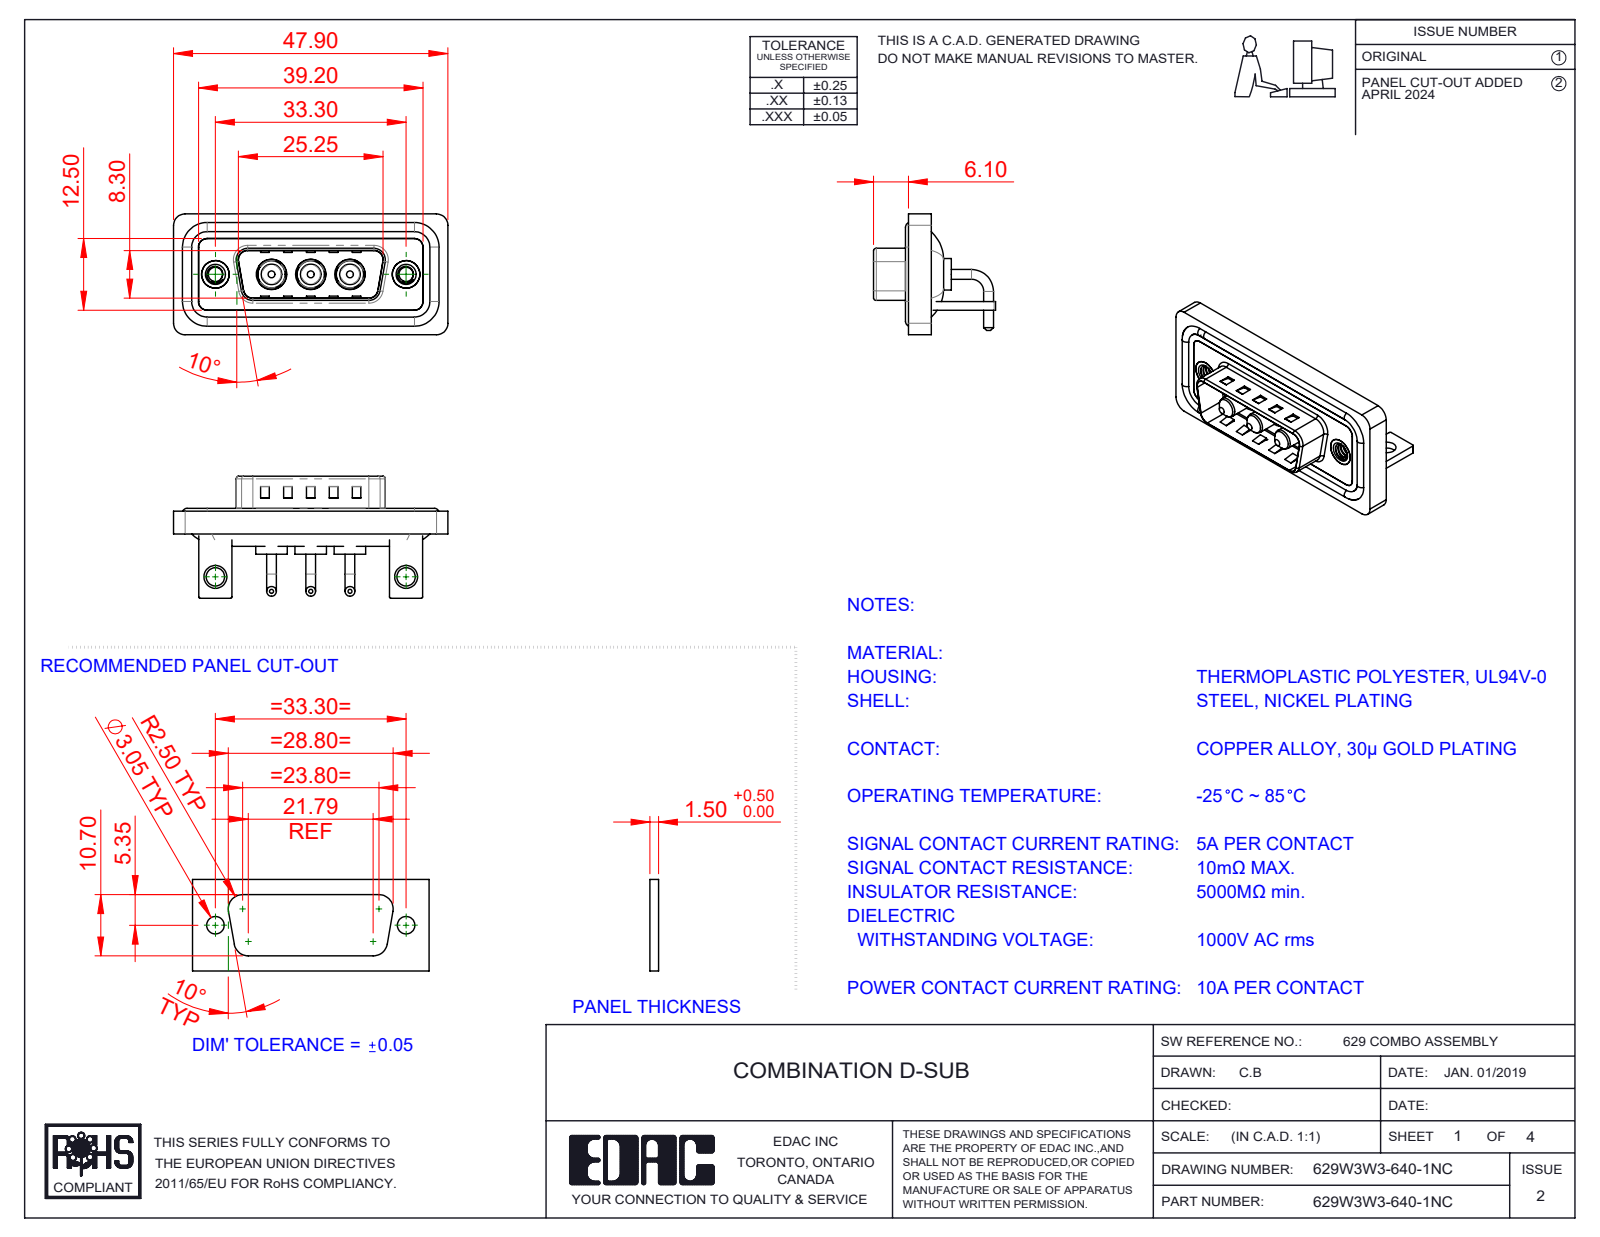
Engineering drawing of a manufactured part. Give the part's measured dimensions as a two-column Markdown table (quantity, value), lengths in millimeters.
| quantity | value |
| --- | --- |
| part name | 629Combo Stabilizer Bracket; 629Combo Housing_3W3; 629Combo Shell Rear_15 Contacts; Power Pin_10A RA (+4 more) |
| STEP written by | SolidWorks 2023 (CONFIG_CONTROL_DESIGN) |
| units | millimeters |
| bodies | 15 solids, 614 faces (227 planar, 265 cylindrical, 122 other) |
| overall size | 47.9 × 21.3 × 21.1 |
| volume | 5 876 mm³ |
| surface area | 9 471 mm² |
| round holes (diameter × count) | 4.85 × 3, 5.3 × 3, 2.5 × 2, 3.2 × 2, 4 × 2, 4.8 × 2, 5 × 2 |
| round bosses / shafts (diameter × count) | 1.7 × 6, 1.6 × 4, 5.5 × 3, 5.2 × 3, 4.75 × 3, 3.75 × 3, 3.6 × 3, 4.9 × 2 |
| partial cylindrical surfaces (radius × count) | 2 × 21, 1.5 × 18, 0.25 × 16, 0.5 × 9, 1.6 × 8, 0.6 × 4, 0.65 × 4, 0.9 × 4 |
| main face-to-face distances | 0.4, 1.5, 0.8, 2.9, 1.1, 2.1, 3.7, 1.6, 1.2, 4.5 |
| hole center spacings | 6.85, 9.8, 16.65, 23.5, 33.3, 13.7 |
